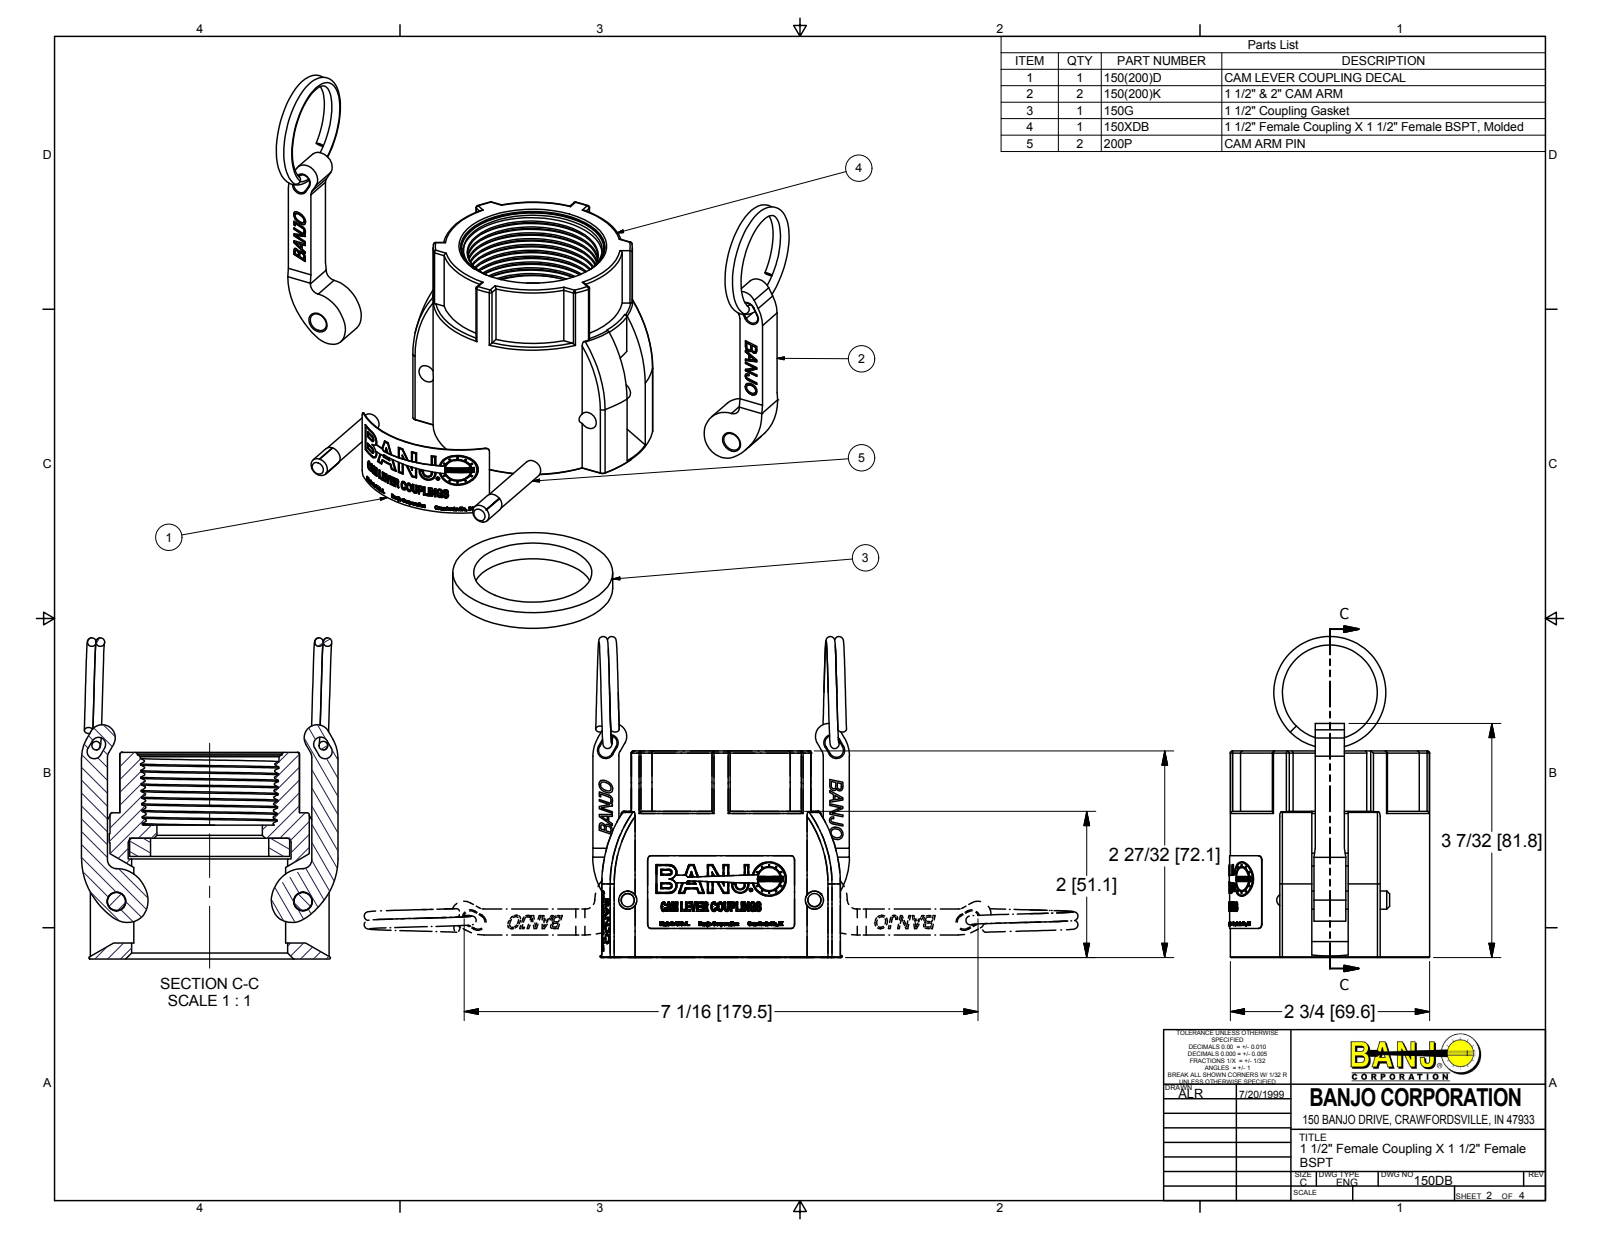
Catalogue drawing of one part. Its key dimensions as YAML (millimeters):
part_name: "150XDB; 150(200)XK; 150RING; 150(200)K (+4 more)"
step_written_by: "Autodesk Inventor 2016 (AUTOMOTIVE_DESIGN)"
units: millimeters
bodies: {solids: 9, faces: 2024, planar: 976, cylindrical: 266, other: 782}
overall_size: [112.12, 89.57, 69.98]
volume: 149860
surface_area: 58778
round_holes:
  - {diameter: 6.35, count: 2}
  - {diameter: 6.55, count: 2}
  - {diameter: 8.07, count: 1}
  - {diameter: 11.4, count: 1}
  - {diameter: 36.83, count: 1}
  - {diameter: 41.27, count: 1}
  - {diameter: 50.46, count: 1}
  - {diameter: 54.48, count: 1}
  - {diameter: 56.9, count: 1}
round_bosses_or_shafts:
  - {diameter: 6.6, count: 2}
  - {diameter: 6.32, count: 2}
  - {diameter: 69.6, count: 1}
  - {diameter: 55.88, count: 1}
  - {diameter: 49.7, count: 1}
  - {diameter: 12, count: 1}
partial_cylinders:
  - {radius: 0.76, count: 19}
  - {radius: 1.52, count: 8}
  - {radius: 2.48, count: 4}
  - {radius: 0.7, count: 2}
  - {radius: 1, count: 2}
  - {radius: 2.35, count: 2}
  - {radius: 2.65, count: 2}
  - {radius: 3.15, count: 2}
face_to_face_distances: [42.17, 6.35, 11.94, 11.18, 23.88, 35.82, 29.97, 12.7, 36.32, 72.14]
hole_center_spacings: [17.45, 49.91, 65.18]
